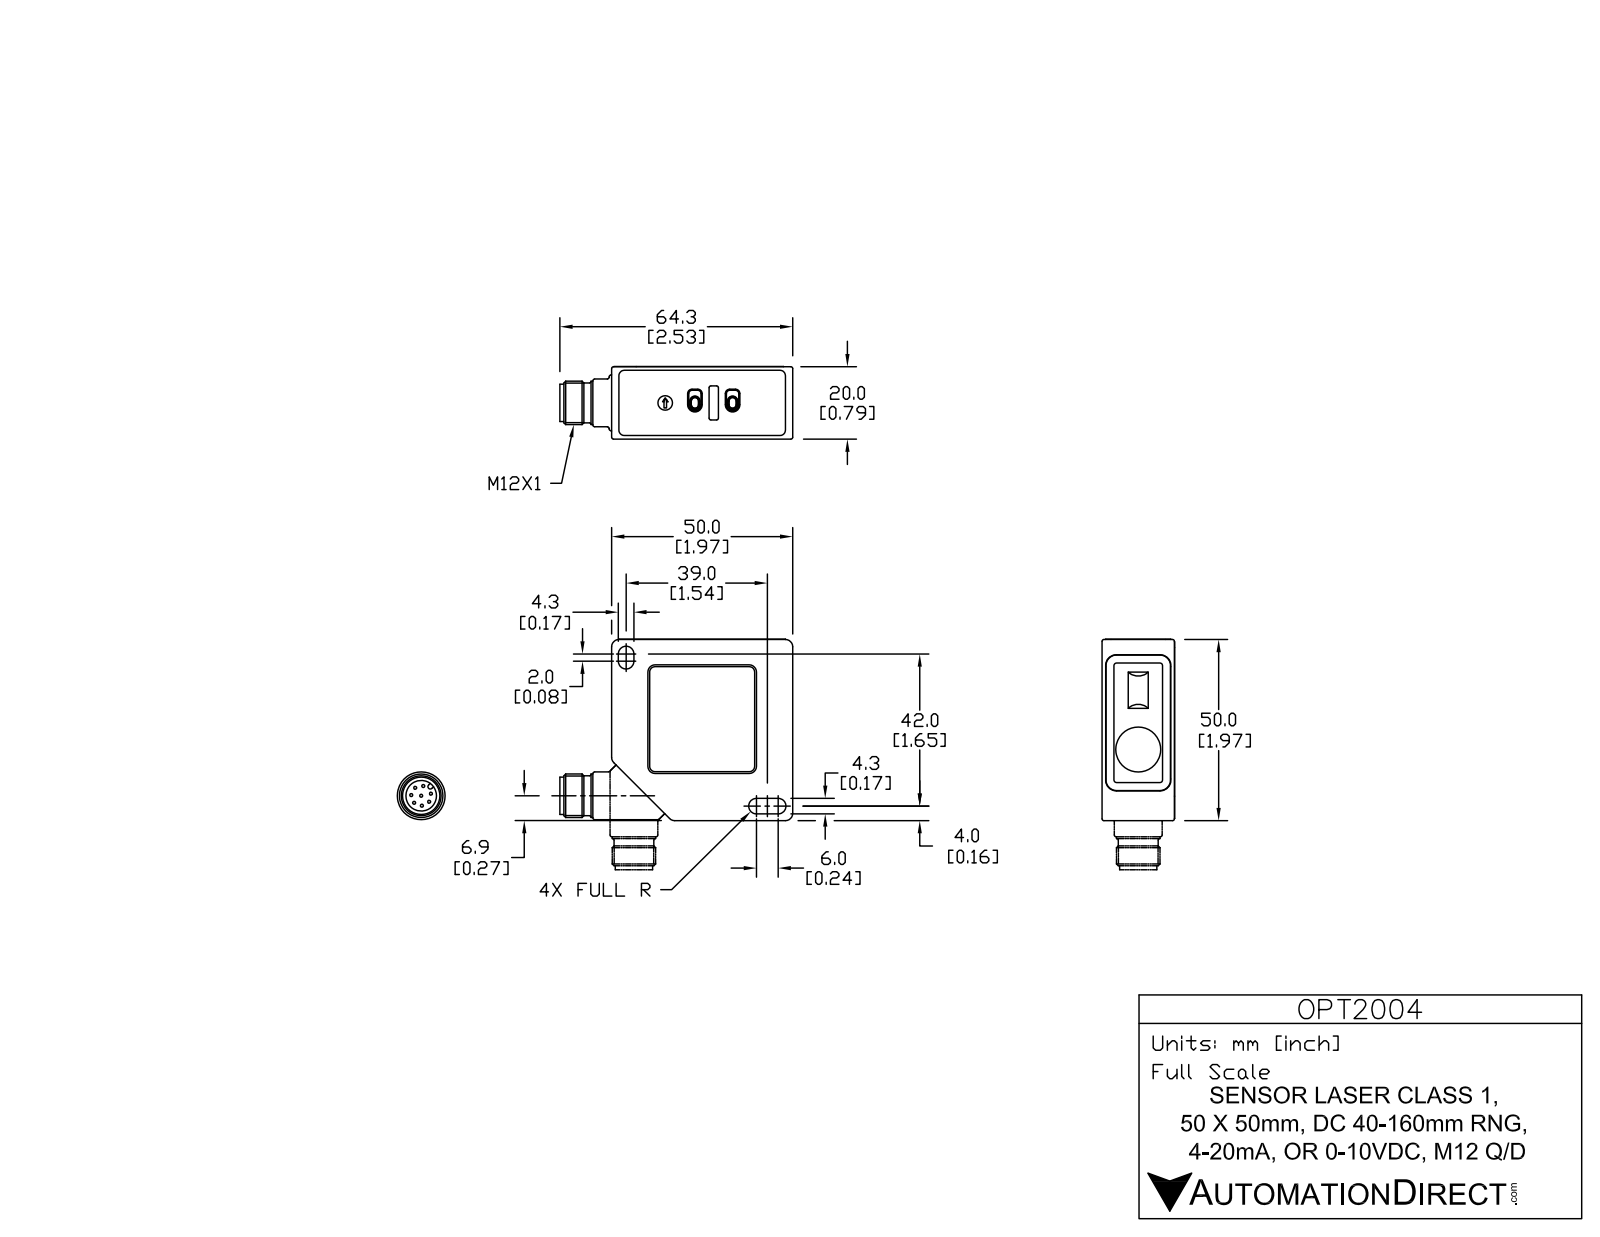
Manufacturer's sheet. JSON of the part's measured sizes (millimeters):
{"part_name": "OPT2004", "step_written_by": "SolidWorks 2013 (AUTOMOTIVE_DESIGN)", "units": "millimeters", "bodies": {"solids": 15, "faces": 301, "planar": 153, "cylindrical": 134, "other": 14}, "overall_size": [64.43, 50.1, 20], "volume_mm3": 48653, "surface_area_mm2": 16026, "round_holes": [[4, 1], [8.45, 1]], "round_bosses_or_shafts": [[0.82, 8], [18, 1], [13.5, 1], [12.39, 1], [12, 1], [11, 1], [10.3, 1]], "partial_cylinders_radius": [[2, 17], [0.2, 10], [1, 8], [2.1, 5], [0.5, 4], [1.2, 4], [2.15, 4], [2.9, 4]], "face_to_face_distances": [20, 19.8, 50, 50.1, 48.3, 1.6, 48.4, 5.33, 53.63, 53.73]}
